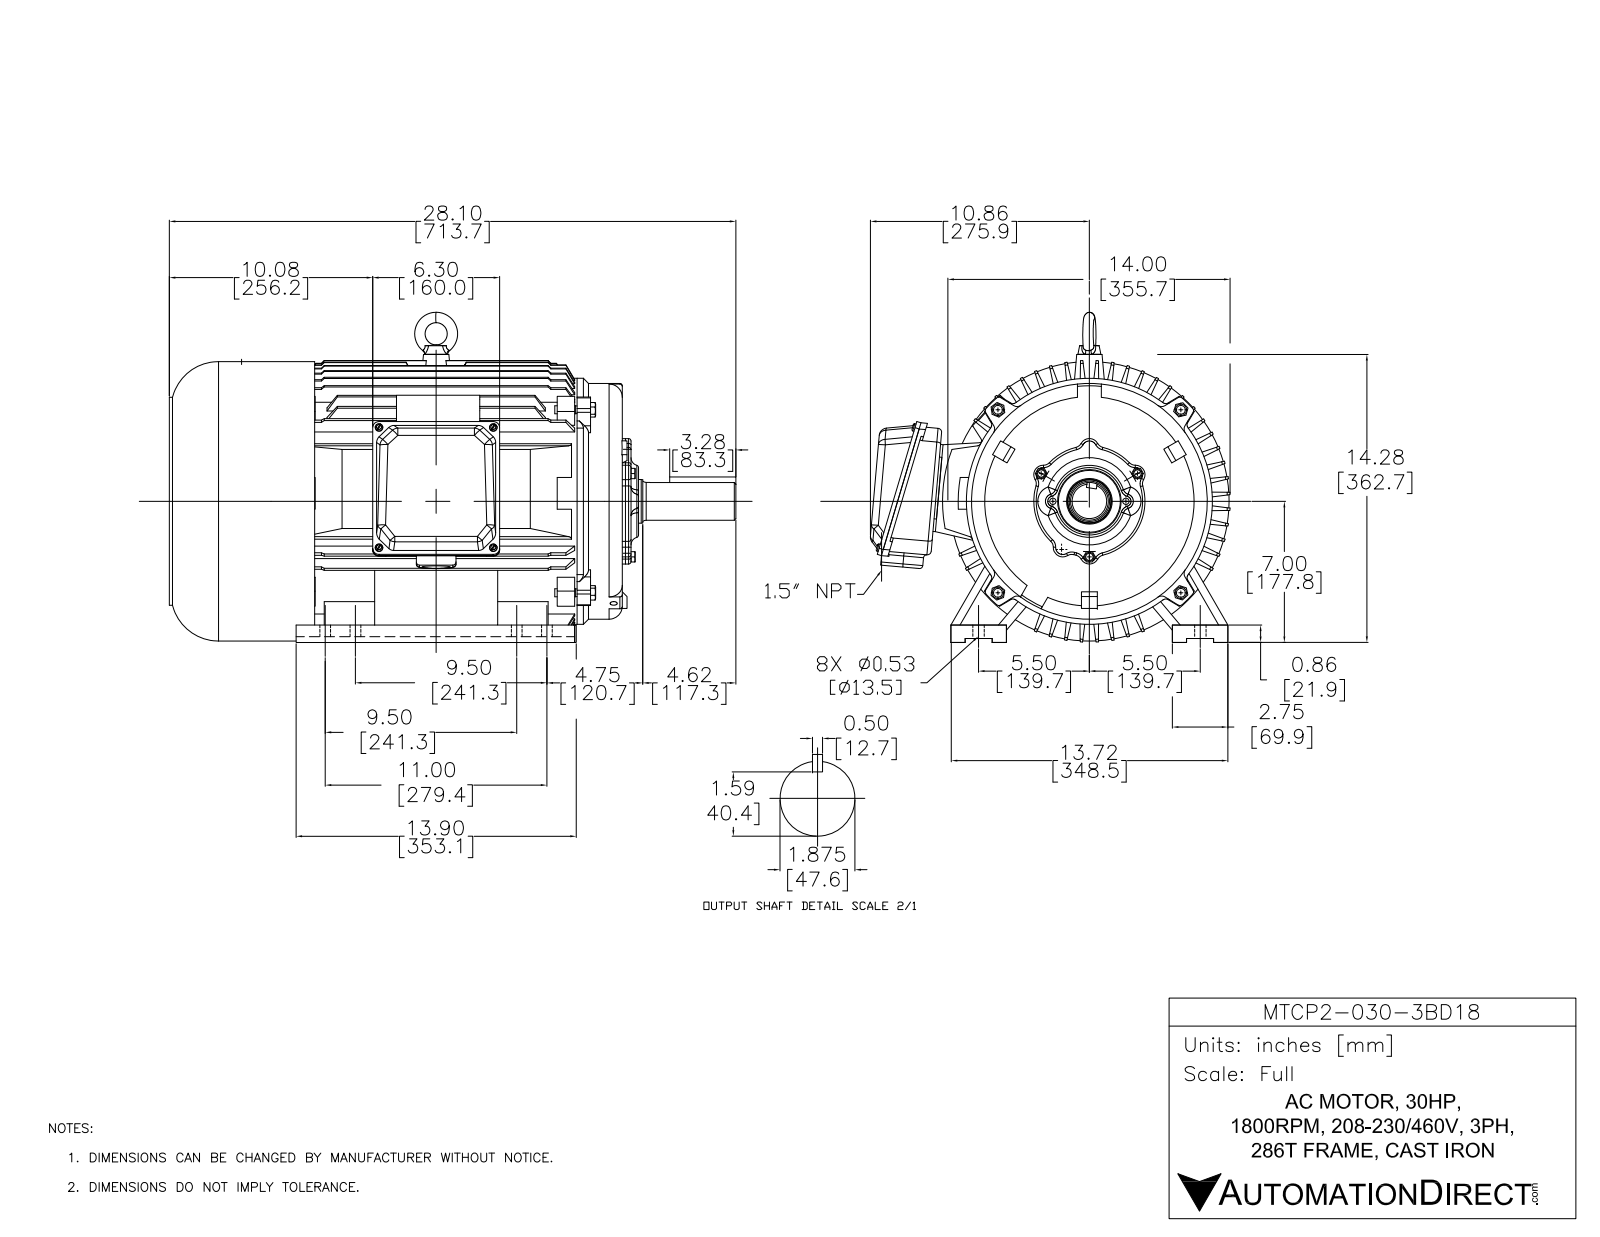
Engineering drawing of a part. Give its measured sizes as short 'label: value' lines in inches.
name: PEWWE-286T-4,6,8
written by: SolidWorks 2017 (AUTOMOTIVE_DESIGN)
unit: in
bodies: 20 solids, 4371 faces (2170 planar, 1992 cylindrical, 209 other)
size: 28.1 × 17.844 × 16.374
volume: 1 537 in³; area: 3 594 in²
holes: 8× ⌀0.276, 8× ⌀0.551, 7× ⌀0.394, 4× ⌀0.197, 4× ⌀0.236, 4× ⌀0.441, 4× ⌀0.472, 3× ⌀0.362, 2× ⌀0.315, 2× ⌀0.354, 1× ⌀0.335, 1× ⌀0.669
bosses: 4× ⌀0.355, 4× ⌀0.197, 3× ⌀0.315, 3× ⌀0.283, 1× ⌀13.858, 1× ⌀12.205, 1× ⌀11.693, 1× ⌀10.315
rounds: 1248× R0.02, 38× R0.157, 26× R0.394, 24× R0.315, 13× R0.197, 5× R0.472, 4× R0.63, 1× R0.984
face distances: 0.197, 0.866, 0.315, 0.472, 15.262, 22.467, 7.205, 0.394, 0.236, 0.669
hole spacings: 5.669, 6.22, 2.953, 8.416, 11, 1.5, 2.756, 2.959
